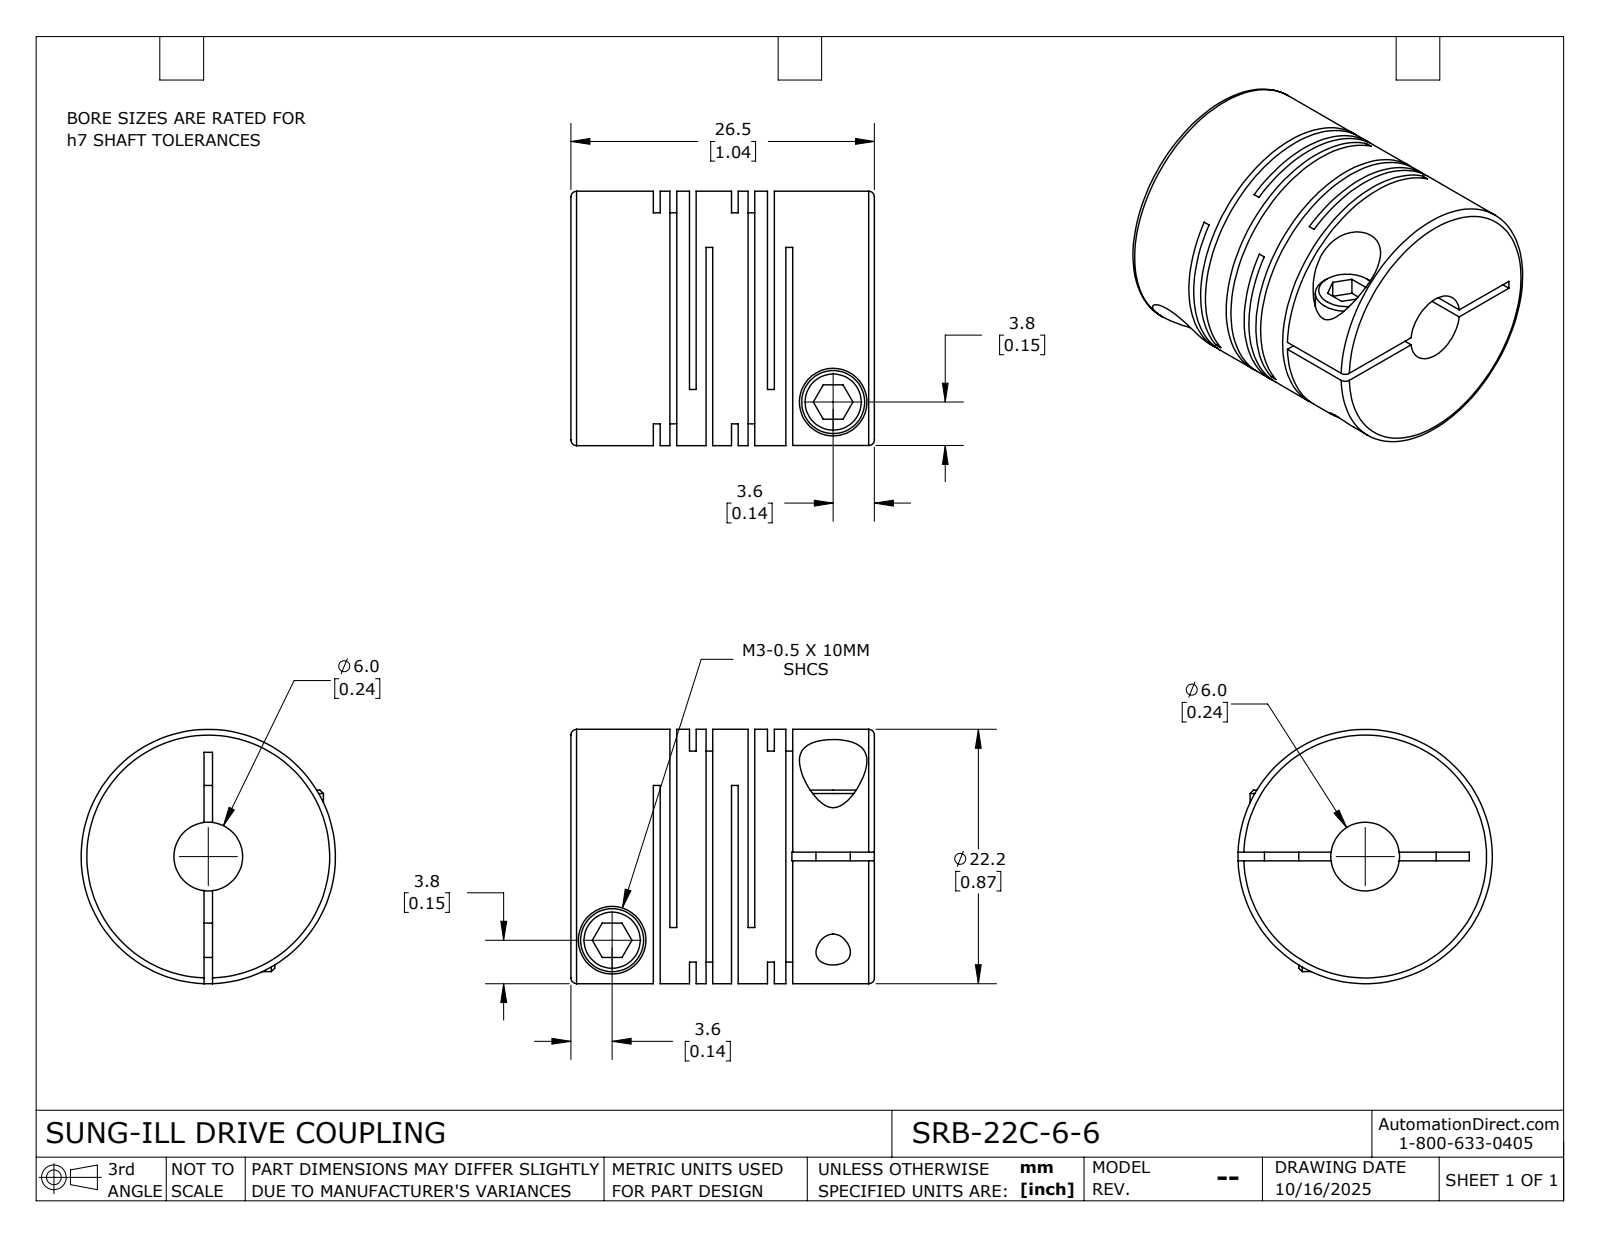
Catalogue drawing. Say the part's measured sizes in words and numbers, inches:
The part is named "SRB-22C-6-6". Its 3-D file was written by "SolidWorks 2024 (CONFIG_CONTROL_DESIGN)". It is 1 solid with 115 faces: 60 planar, 42 cylindrical and 13 other. Overall it measures 1.043 by 0.874 by 0.874 inches. Its volume is 0.474 cubic inches and its surface area 12.63 square inches. Round holes: 2 of diameter 0.118, 2 of diameter 0.232, 1 of diameter 0.236. Round bosses or shafts: 2 of diameter 0.217, 1 of diameter 0.874. The main face-to-face distances are 0.023, 0.269, 0.124, 0.057, 0.211, 0.067, 0.144, 0.245, 0.034, 0.101.
